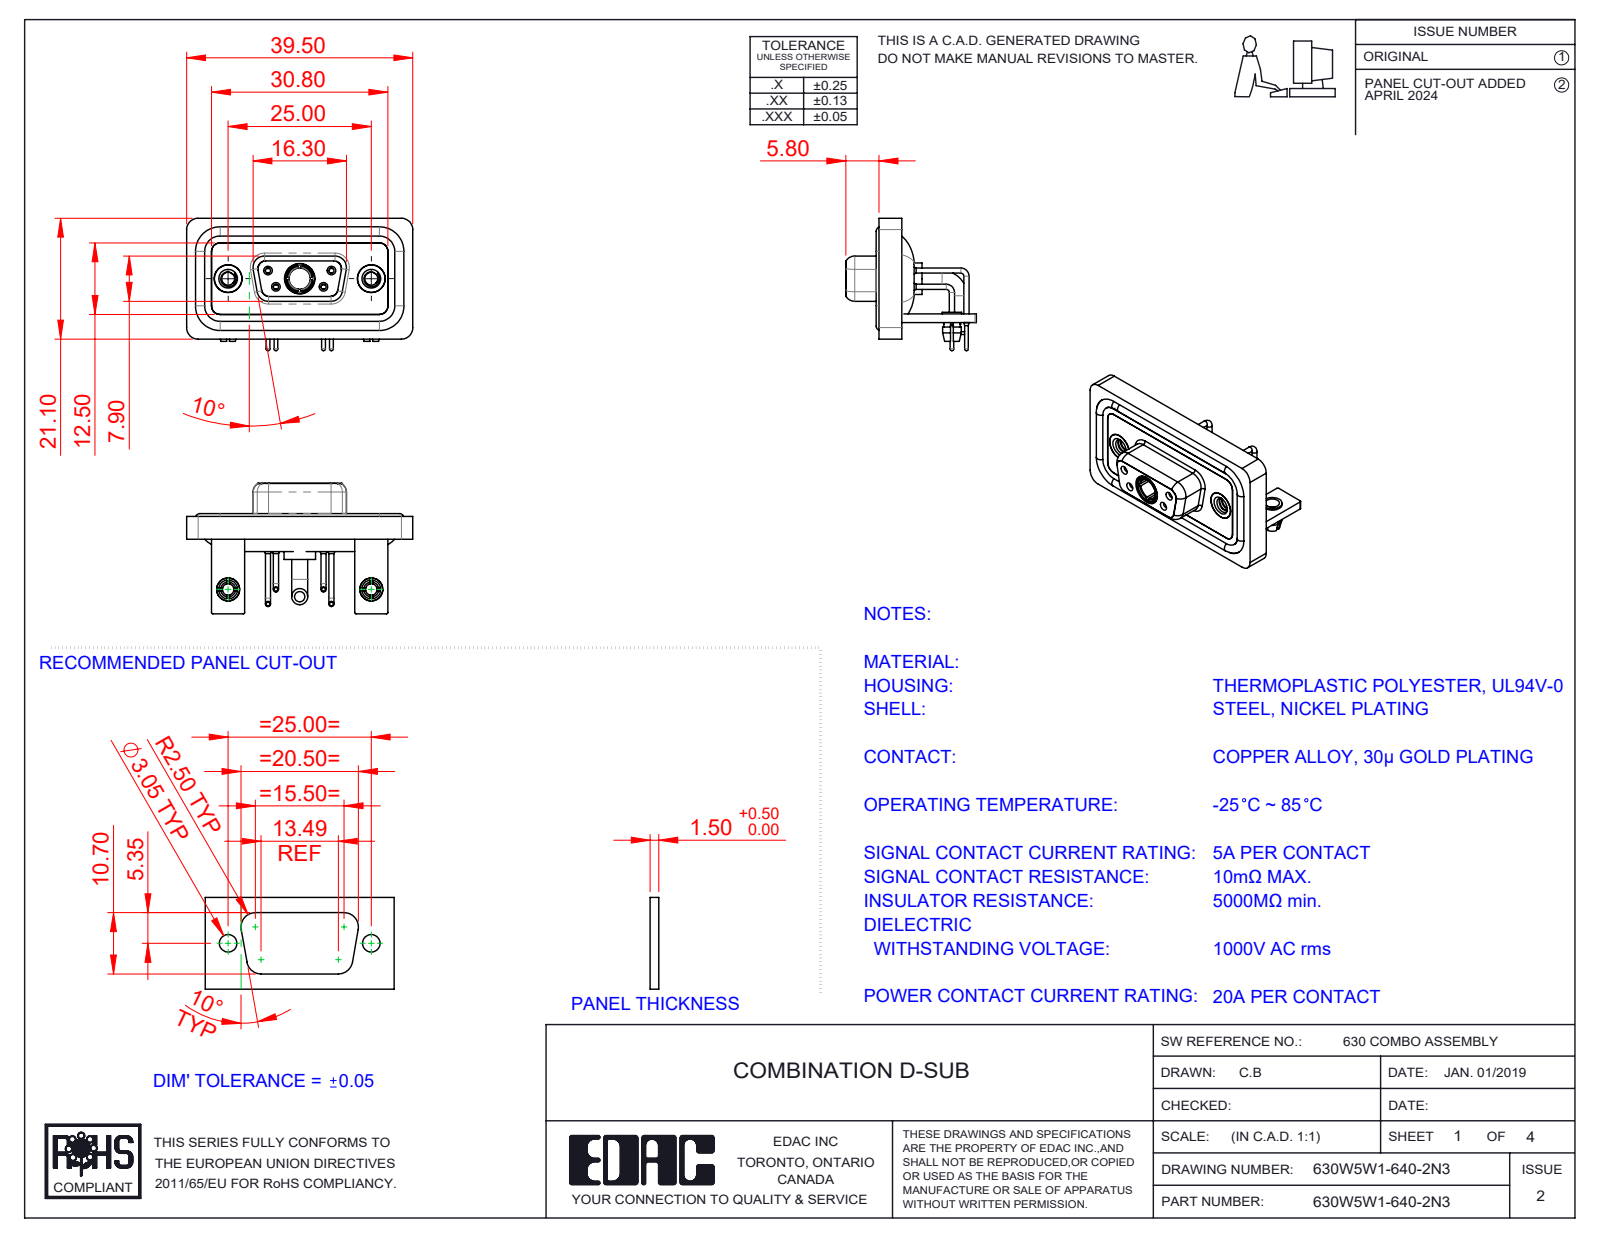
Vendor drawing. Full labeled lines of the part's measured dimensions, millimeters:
Part name (STEP PRODUCT): 630Combo Shell Front_09 Contacts; 630Combo Contact Row 2_50 Contacts; 630Combo Threaded Rivet_2; Power Socket_20A RA (+7 more)
STEP written by: SolidWorks 2023 (CONFIG_CONTROL_DESIGN)
Units: millimetres
Bodies: 17 solids, 816 faces (262 planar, 361 cylindrical, 193 other)
Overall size (bounding box): 39.5 × 23.12 × 22.8
Volume: 5 231 mm³ · Surface area: 8 789 mm²
Round holes (diameter × count): ⌀2 ×6, ⌀0.9 ×4, ⌀1.1 ×4, ⌀1.5 ×4, ⌀4.85 ×3, ⌀1.6 ×2, ⌀1.7 ×2, ⌀2.26 ×2, ⌀2.5 ×2, ⌀3.2 ×2, ⌀4 ×2, ⌀4.05 ×2
Round bosses / shafts (diameter × count): ⌀1.6 ×6, ⌀0.9 ×4, ⌀0.65 ×4, ⌀4.95 ×2, ⌀4.8 ×2, ⌀4 ×2, ⌀3.4 ×2, ⌀3.3 ×2
Partial cylindrical surfaces — rounded edges, fillets, slot ends (radius × count): R2 ×19, R1.5 ×18, R0.25 ×16, R1.35 ×8, R1.6 ×8, R0.5 ×5, R0.6 ×4, R0.65 ×4
Main face-to-face distances: 0.4, 2.9, 1.5, 1.8, 1.1, 3.7, 1.6, 0.8, 2.5, 3.1
Hole centre spacings: 3.16, 5.72, 7.1, 12.5, 18.1, 25, 4.39, 4.4
